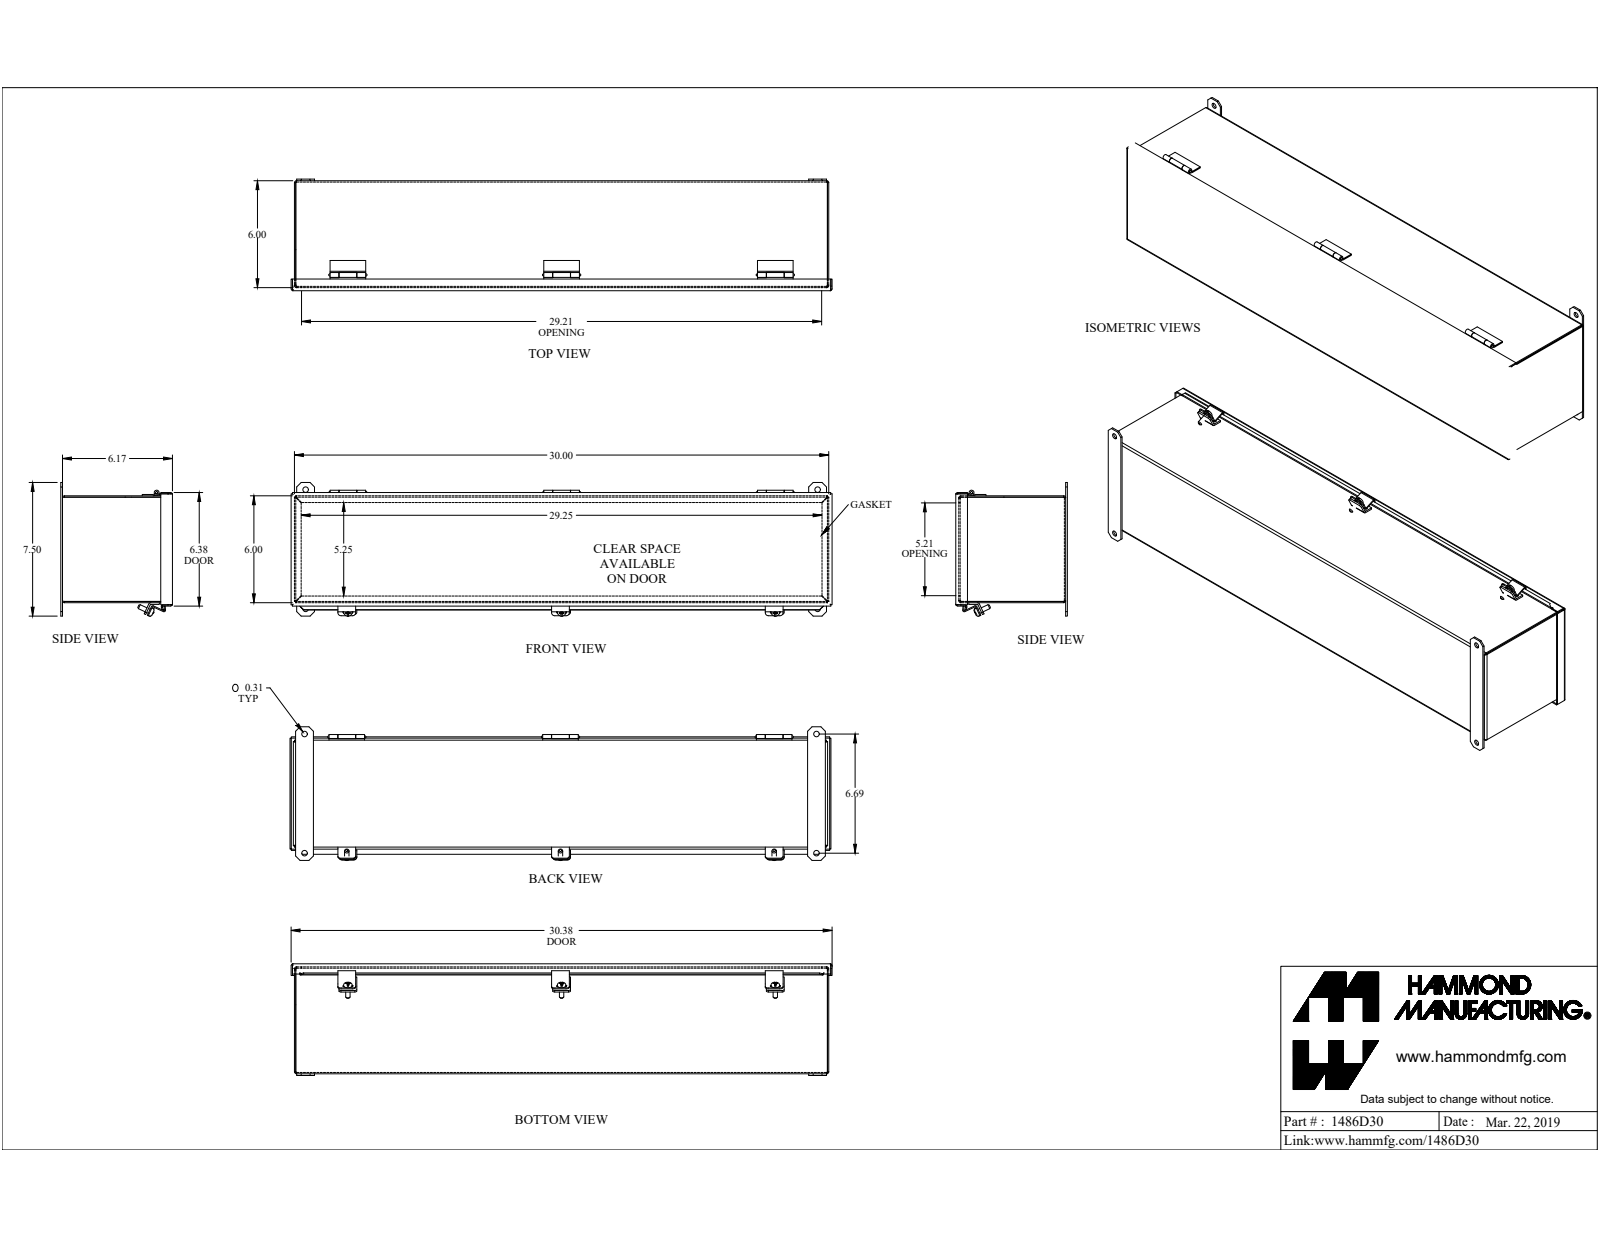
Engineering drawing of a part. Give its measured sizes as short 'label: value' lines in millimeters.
name: 1486D30
written by: SolidWorks 2019 (CONFIG_CONTROL_DESIGN)
unit: mm
bodies: 26 solids, 536 faces (355 planar, 124 cylindrical, 57 other)
size: 771.5 × 190.7 × 159.2
volume: 1 225 000 mm³; area: 1 256 000 mm²
holes: 4× ⌀8, 3× ⌀5.4, 1× ⌀3.2
bosses: 3× ⌀12.2, 3× ⌀6.2, 1× ⌀7, 1× ⌀3.2
rounds: 13× R0.9, 13× R2.7, 12× R4.8, 12× R6.4, 6× R0.3, 6× R3.6, 2× R0.7, 2× R2.2
face distances: 1.8, 150.6, 154.9, 152.4, 148.7, 156.8, 153.1, 4.7, 760.2, 6.6
hole spacings: 169.9, 304.8, 609.6, 730.3, 730.3, 749.7, 749.8
